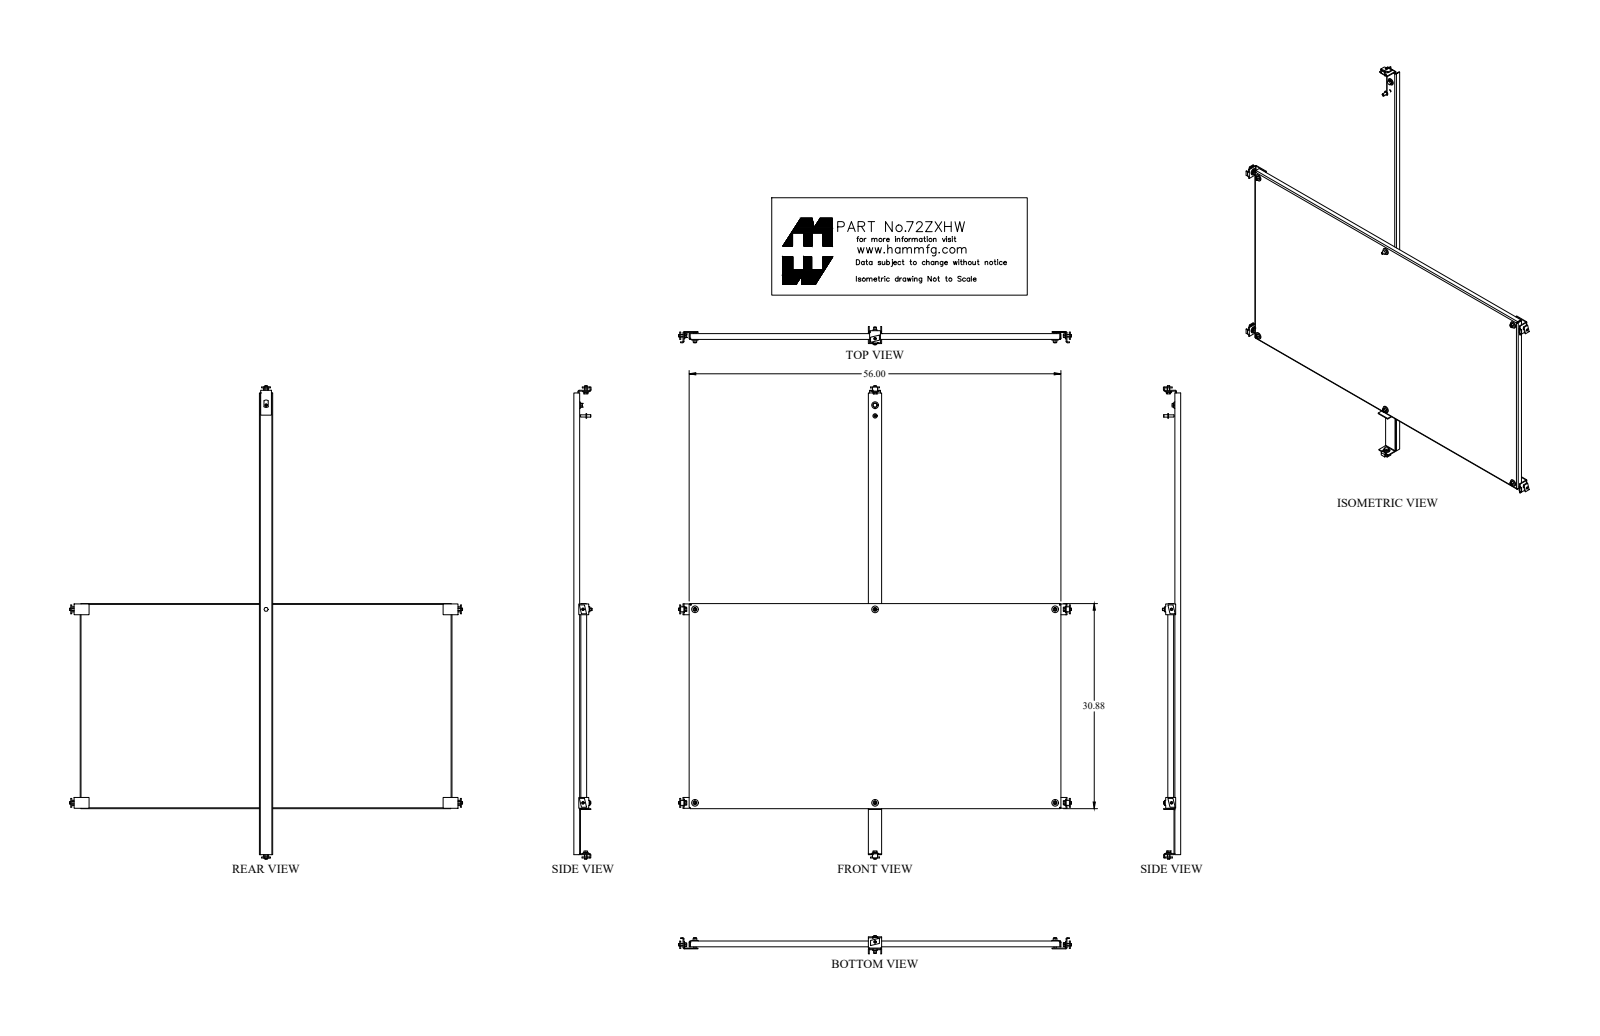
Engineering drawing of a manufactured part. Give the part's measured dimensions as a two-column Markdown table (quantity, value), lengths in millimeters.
| quantity | value |
| --- | --- |
| part name | 72ZXHW_Default |
| STEP written by | SolidWorks 2018 (CONFIG_CONTROL_DESIGN) |
| units | millimeters |
| bodies | 1 solid, 60 faces (34 planar, 20 cylindrical, 6 other) |
| overall size | 1422.4 × 784.2 × 22.2 |
| volume | 3 785 000 mm³ |
| surface area | 2 399 000 mm² |
| round holes (diameter × count) | 14.3 × 6 |
| partial cylindrical surfaces (radius × count) | 1.5 × 4, 4.7 × 4 |
| main face-to-face distances | 3.2, 781.1, 3.2, 1419.2, 777.9, 784.2, 22.2, 19.1, 1416.1, 1422.4 |
| hole center spacings | 689, 1010.9, 739.8, 1378, 1564 |
